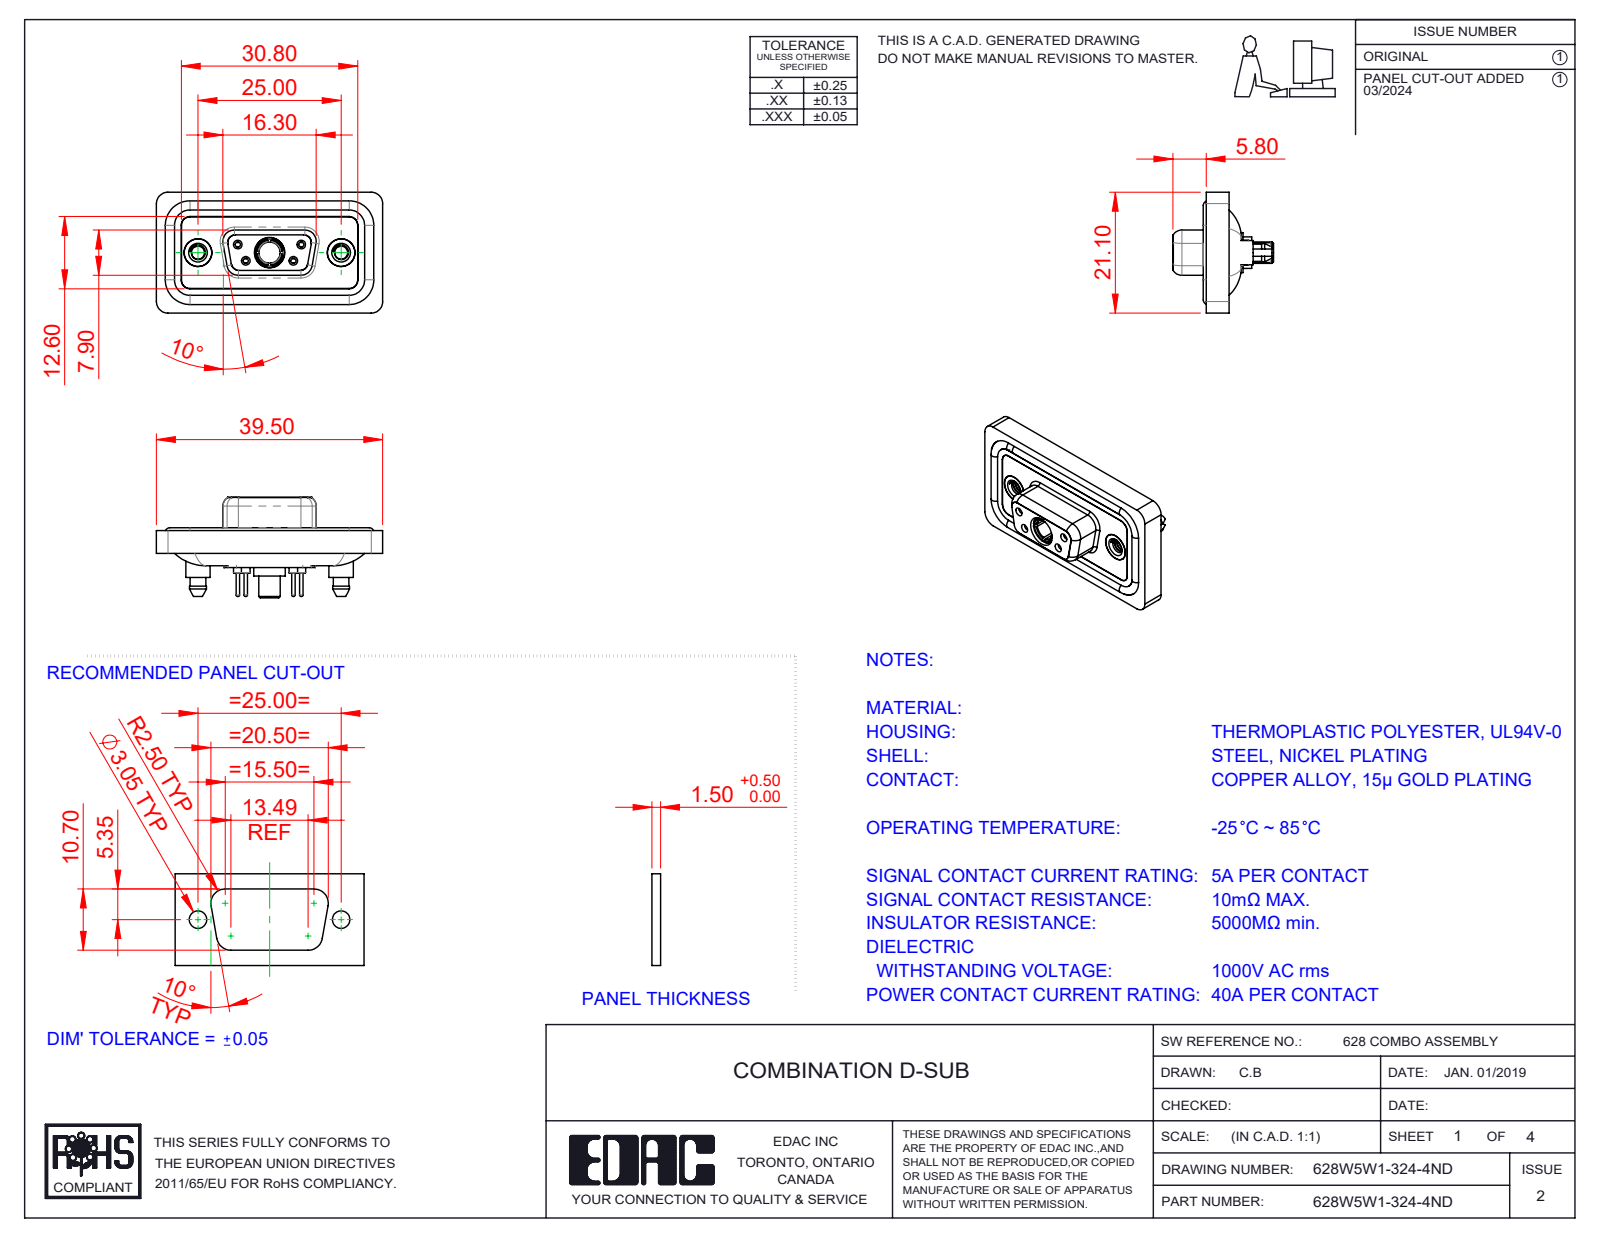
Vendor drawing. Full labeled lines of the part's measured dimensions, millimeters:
Part name (STEP PRODUCT): 628W5W1-324-4ND; 628Combo Contact Row 1_24; 628Combo Waterproof Housing_09 Contacts; Power Socket_40A S (+5 more)
STEP written by: SolidWorks 2023 (CONFIG_CONTROL_DESIGN)
Units: millimetres
Bodies: 13 solids, 746 faces (210 planar, 335 cylindrical, 201 other)
Overall size (bounding box): 39.5 × 21.1 × 17.55
Volume: 4 921 mm³ · Surface area: 7 985 mm²
Round holes (diameter × count): ⌀0.9 ×4, ⌀1.1 ×4, ⌀1.5 ×4, ⌀2 ×4, ⌀4.85 ×3, ⌀1.6 ×2, ⌀1.7 ×2, ⌀2.26 ×2, ⌀4 ×2, ⌀4.05 ×2, ⌀5 ×2, ⌀3.7 ×1
Round bosses / shafts (diameter × count): ⌀1.6 ×6, ⌀2.2 ×4, ⌀0.6 ×4, ⌀5.4 ×2, ⌀4.95 ×2, ⌀4.8 ×2, ⌀4.25 ×2, ⌀5.5 ×1
Partial cylindrical surfaces — rounded edges, fillets, slot ends (radius × count): R1.5 ×24, R2 ×18, R1.6 ×10, R1.35 ×8, R0.25 ×4, R0.5 ×4, R0.6 ×4, R0.65 ×4
Main face-to-face distances: 0.4, 2.9, 1.1, 1.8, 1.6, 0.5, 5.65, 7.45, 5.35, 3.6
Hole centre spacings: 3.16, 5.72, 7.1, 12.5, 18.1, 4.39, 4.4, 8.31
